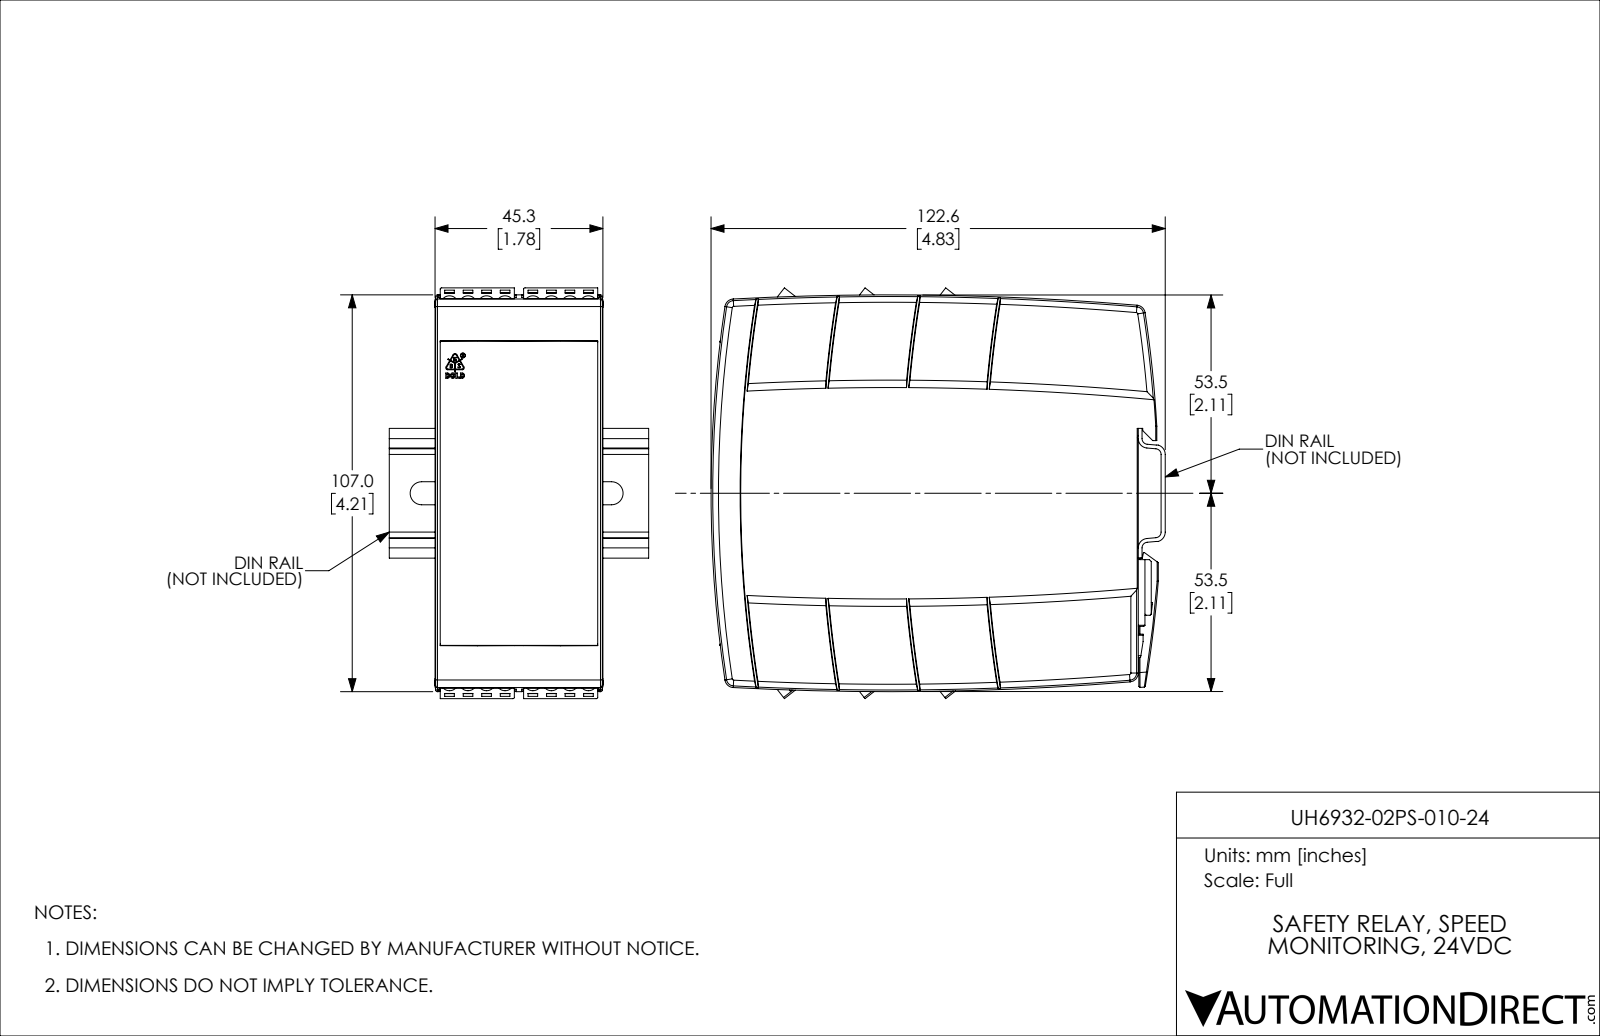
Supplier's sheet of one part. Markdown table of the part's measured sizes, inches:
| quantity | value |
| --- | --- |
| part name | UH6932-02PS-010-24 |
| STEP written by | SolidWorks 2018 (AUTOMOTIVE_DESIGN) |
| units | inches |
| bodies | 13 solids, 9557 faces (7531 planar, 1760 cylindrical, 266 other) |
| overall size | 4.752 × 4.362 × 1.783 |
| volume | 6.596 in³ |
| surface area | 185.9 in² |
| round holes (diameter × count) | 0.059 × 48, 0.126 × 48, 0.157 × 48, 0.029 × 6, 0.032 × 6, 0.049 × 1 |
| round bosses / shafts (diameter × count) | 0.149 × 48, 0.079 × 6, 0.053 × 1 |
| partial cylindrical surfaces (radius × count) | 0.115 × 48, 0.016 × 37, 0.004 × 18, 0.012 × 18, 0.013 × 18, 0.013 × 18, 0.005 × 12, 0.007 × 12 |
| main face-to-face distances | 0.045, 1.722, 1.677, 0.053, 1.73, 1.776, 0.675, 0.886, 1.768, 0.079 |
| hole center spacings | 0.197, 0.394, 0.886, 0.689, 1.083, 1.031, 0.492, 0.563 |
